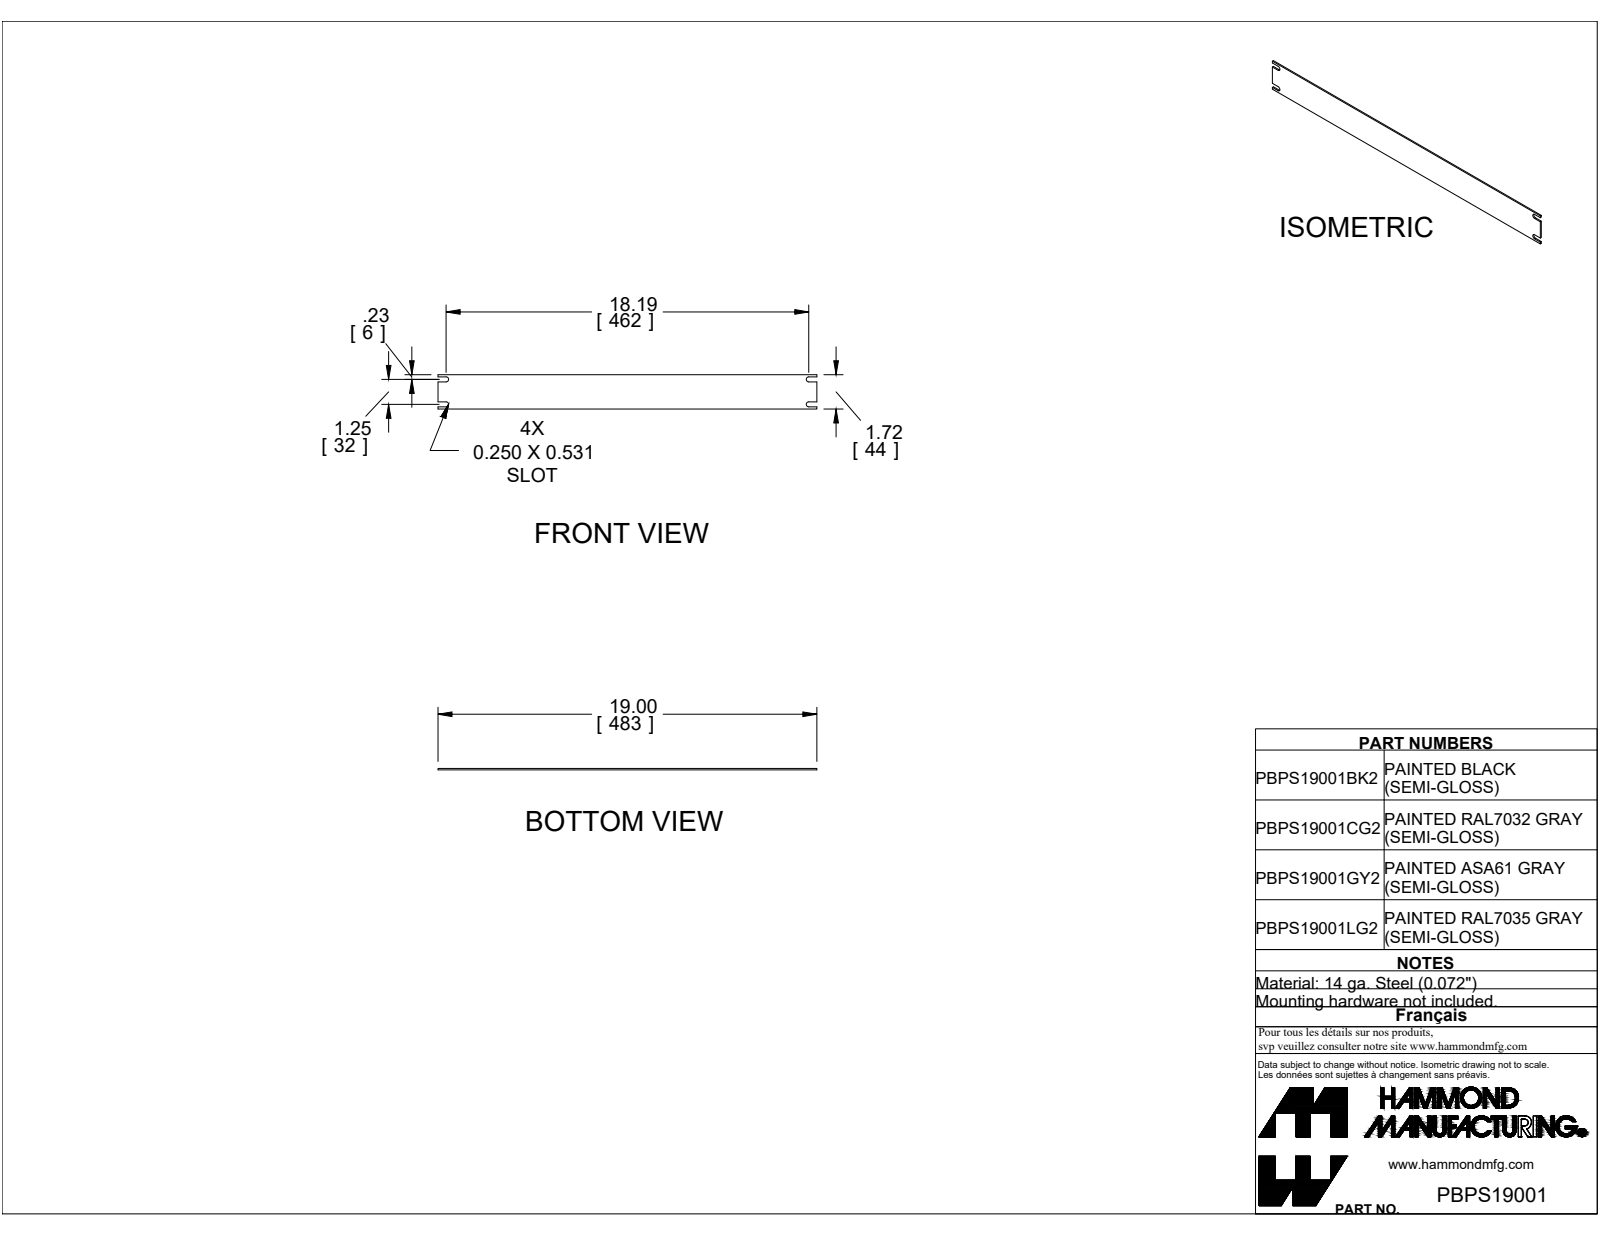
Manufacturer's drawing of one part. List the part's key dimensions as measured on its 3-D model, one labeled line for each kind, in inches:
Part name (STEP PRODUCT): PBPS19001LG2
STEP written by: SolidWorks 2019 (CONFIG_CONTROL_DESIGN)
Units: inches
Bodies: 1 solid, 22 faces (18 planar, 4 cylindrical, 0 other)
Overall size (bounding box): 19 × 1.718 × 0.072
Volume: 2.314 in³ · Surface area: 67.53 in²
Partial cylindrical surfaces — rounded edges, fillets, slot ends (radius × count): R0.125 ×4
Main face-to-face distances: 0.072, 1.718, 0.359, 1.359, 0.109, 1.609, 0.25, 1.25, 19, 1.5
